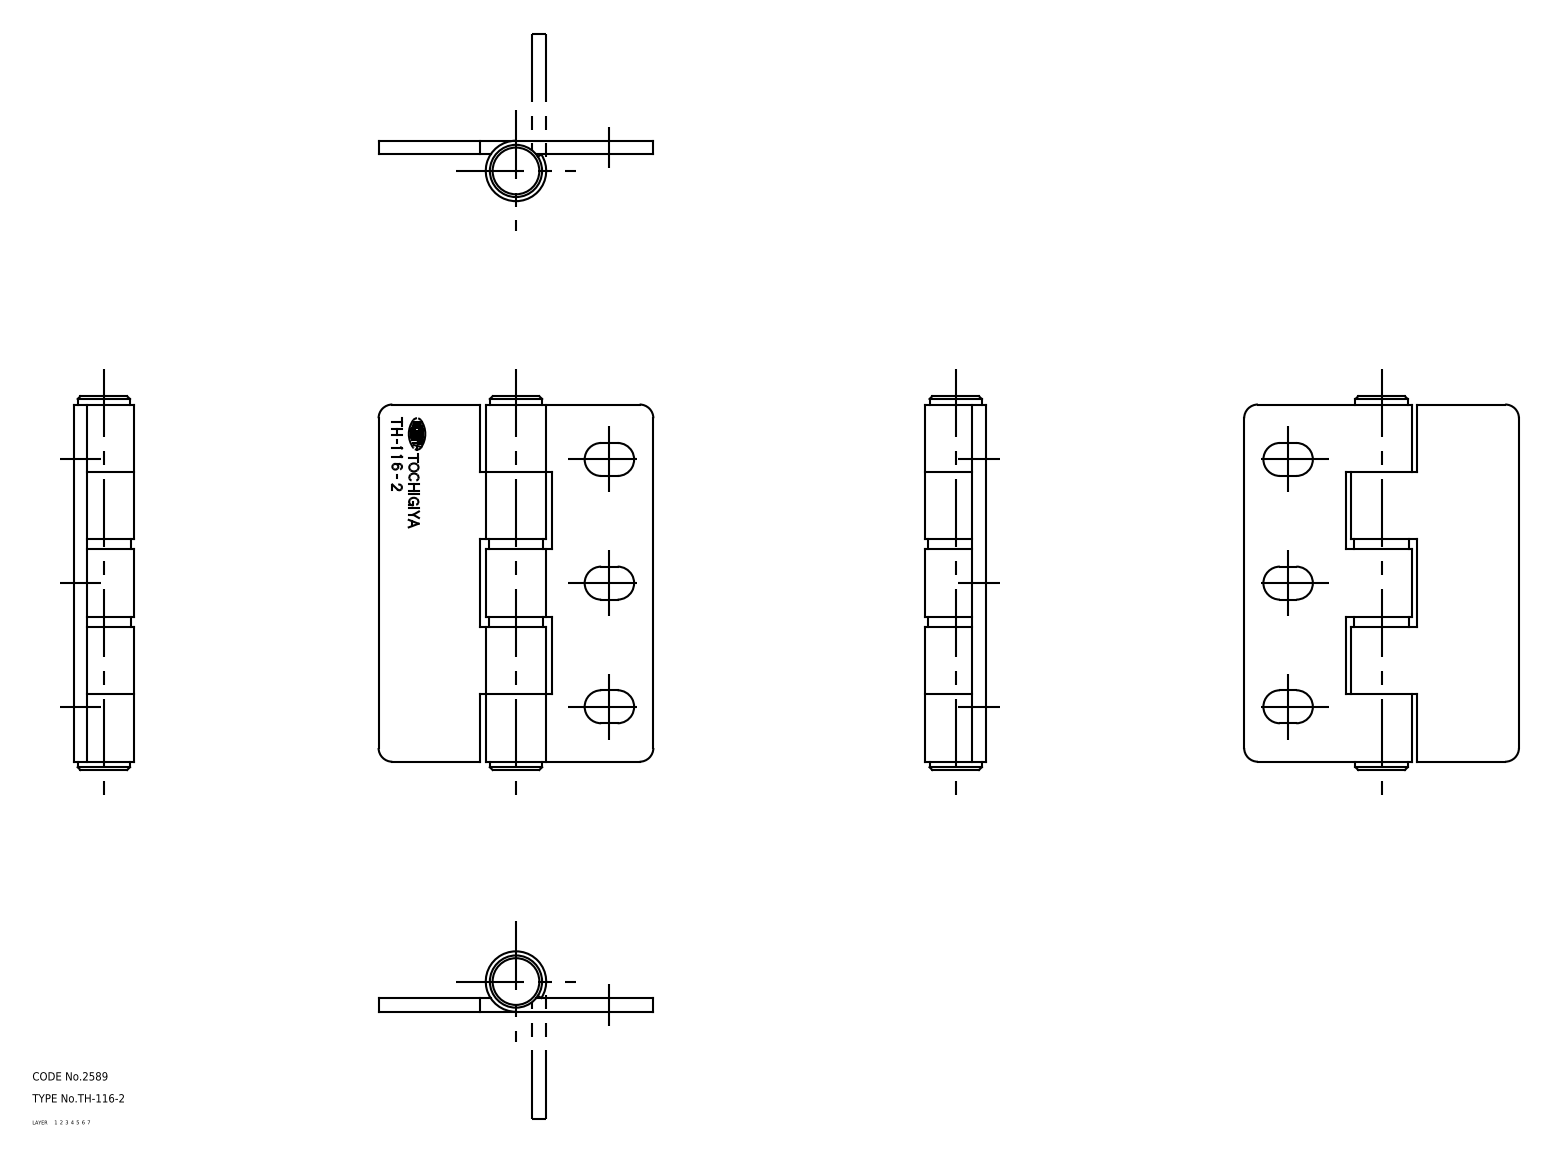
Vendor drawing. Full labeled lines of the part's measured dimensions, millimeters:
Part name (STEP PRODUCT): bearing; cap; shaft; hinge piece_B (+2 more)
STEP written by: CADfix (AUTOMOTIVE_DESIGN)
Units: millimetres
Bodies: 7 solids, 88 faces (0 planar, 0 cylindrical, 88 other)
Overall size (bounding box): 136 × 100 × 22
Volume: 98 623 mm³ · Surface area: 47 332 mm²
